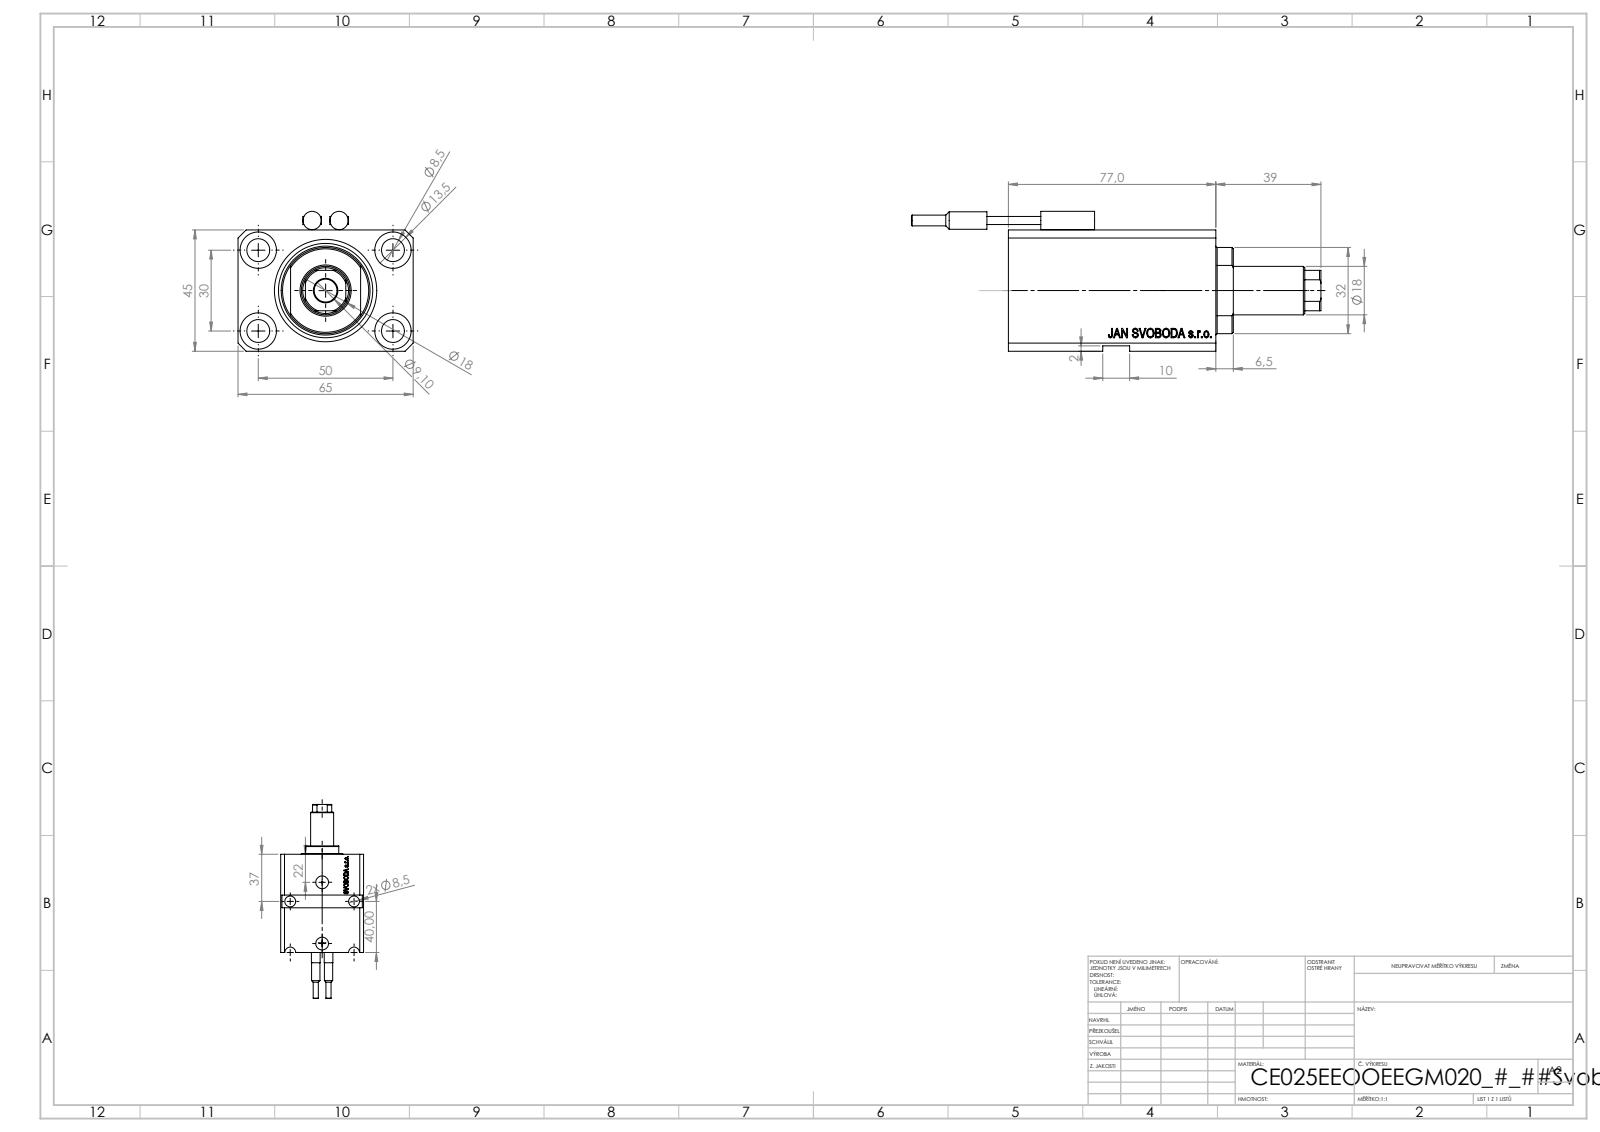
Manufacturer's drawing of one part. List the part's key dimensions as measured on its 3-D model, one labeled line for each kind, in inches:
Part name (STEP PRODUCT): V250CE_E_Body; SWITCH_V250CE; V250CE_VC_E; V250CE_C_VCP
STEP written by: SolidWorks 2019 (CONFIG_CONTROL_DESIGN)
Units: inches
Bodies: 5 solids, 942 faces (466 planar, 90 cylindrical, 386 other)
Overall size (bounding box): 5.984 × 2.559 × 2.043
Volume: 12.82 in³ · Surface area: 83.55 in²
Round holes (diameter × count): ⌀0.335 ×7, ⌀0.531 ×4, ⌀0.049 ×2, ⌀0.394 ×2, ⌀0.709 ×1, ⌀0.984 ×1, ⌀1.496 ×1
Round bosses / shafts (diameter × count): ⌀0.268 ×2, ⌀0.256 ×2, ⌀0.157 ×2
Partial cylindrical surfaces — rounded edges, fillets, slot ends (radius × count): R0.167 ×2, R0.335 ×1, R0.63 ×1
Main face-to-face distances: 1.772, 2.559, 2.043, 3.031, 0.988, 1.26, 0.783, 0.079, 2.677, 0.354
Hole centre spacings: 1.148, 1.969, 1.181, 1.613, 1.63, 2.296, 0.021, 1.869
